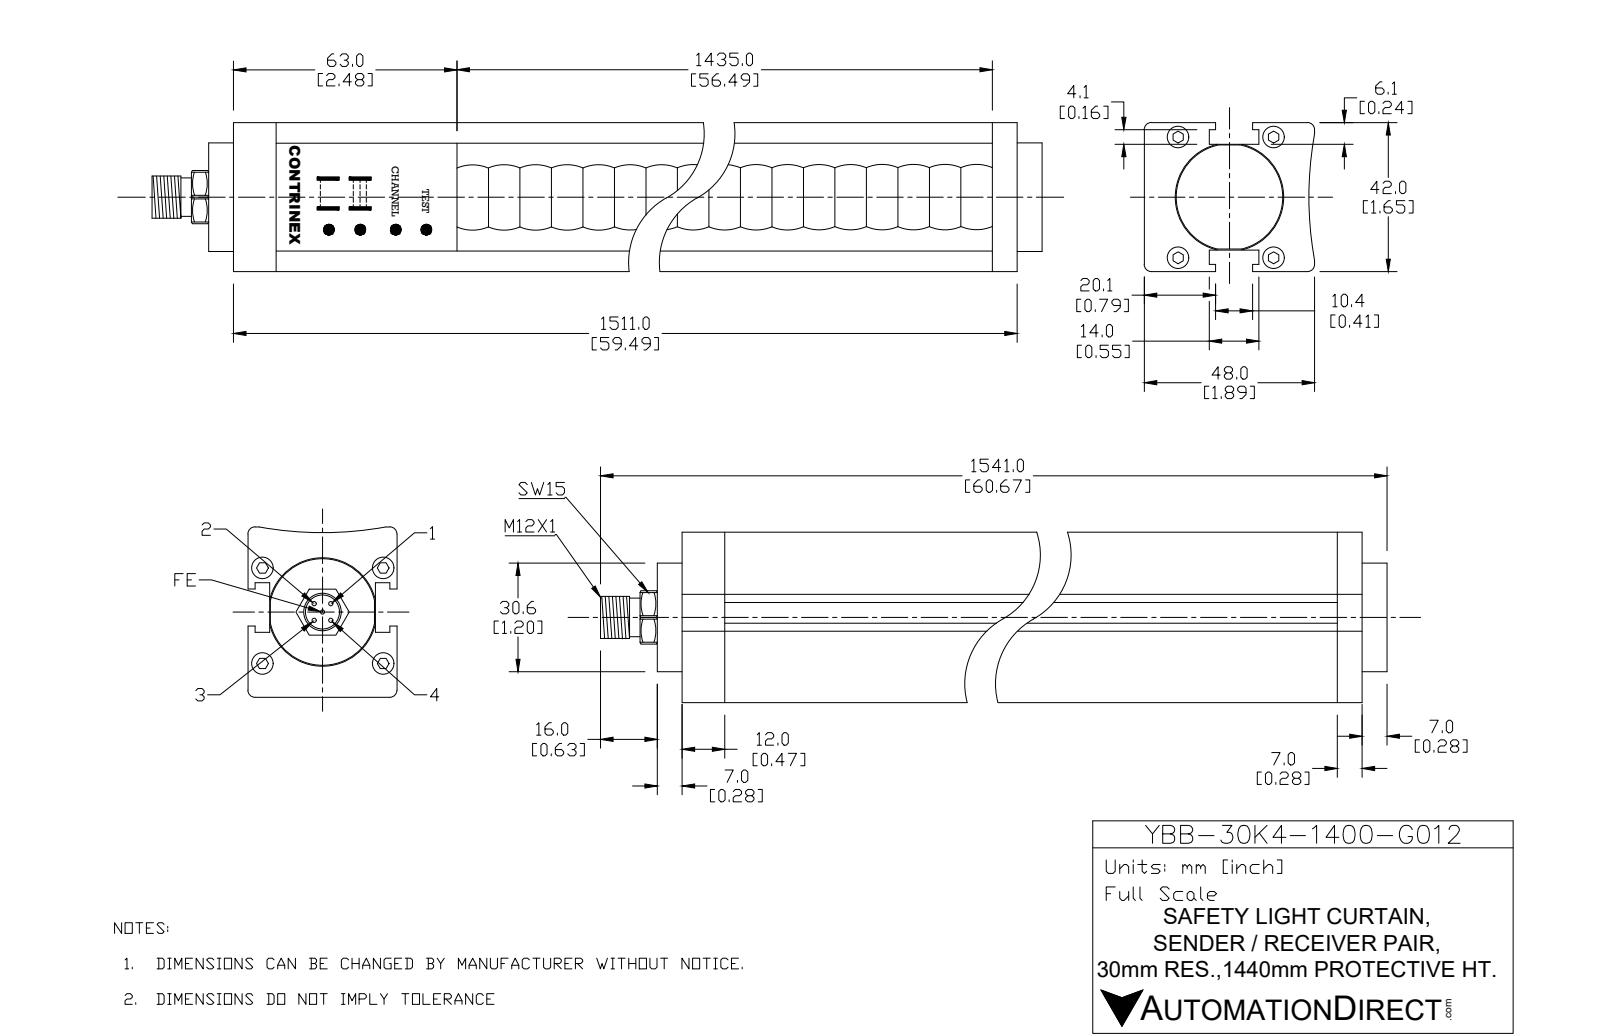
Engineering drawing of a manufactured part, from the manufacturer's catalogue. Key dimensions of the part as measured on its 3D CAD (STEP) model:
Part name (STEP PRODUCT): YBB-30K4-1400-G012
STEP written by: SolidWorks 2019 (AUTOMOTIVE_DESIGN)
Units: inches
Bodies: 1 solid, 533 faces (121 planar, 152 cylindrical, 260 other)
Overall size (bounding box): 60.67 × 1.89 × 1.654
Volume: 155.1 in³ · Surface area: 681.5 in²
Round holes (diameter × count): ⌀0.12 ×4, ⌀0.236 ×4, ⌀0.335 ×1
Round bosses / shafts (diameter × count): ⌀0.039 ×5, ⌀0.217 ×4, ⌀0.119 ×4, ⌀1.205 ×1, ⌀0.472 ×1, ⌀0.413 ×1
Partial cylindrical surfaces — rounded edges, fillets, slot ends (radius × count): R0.035 ×36, R0.039 ×12, R0.016 ×10, R0.217 ×2, R0.02 ×1, R0.02 ×1, R0.323 ×1, R0.689 ×1
Main face-to-face distances: 0.231, 1.422, 1.654, 1.191, 1.827, 2.172, 2.005, 0.2, 1.454, 0.031
Hole centre spacings: 0.828, 0.88, 1.059, 1.339, 1.707
